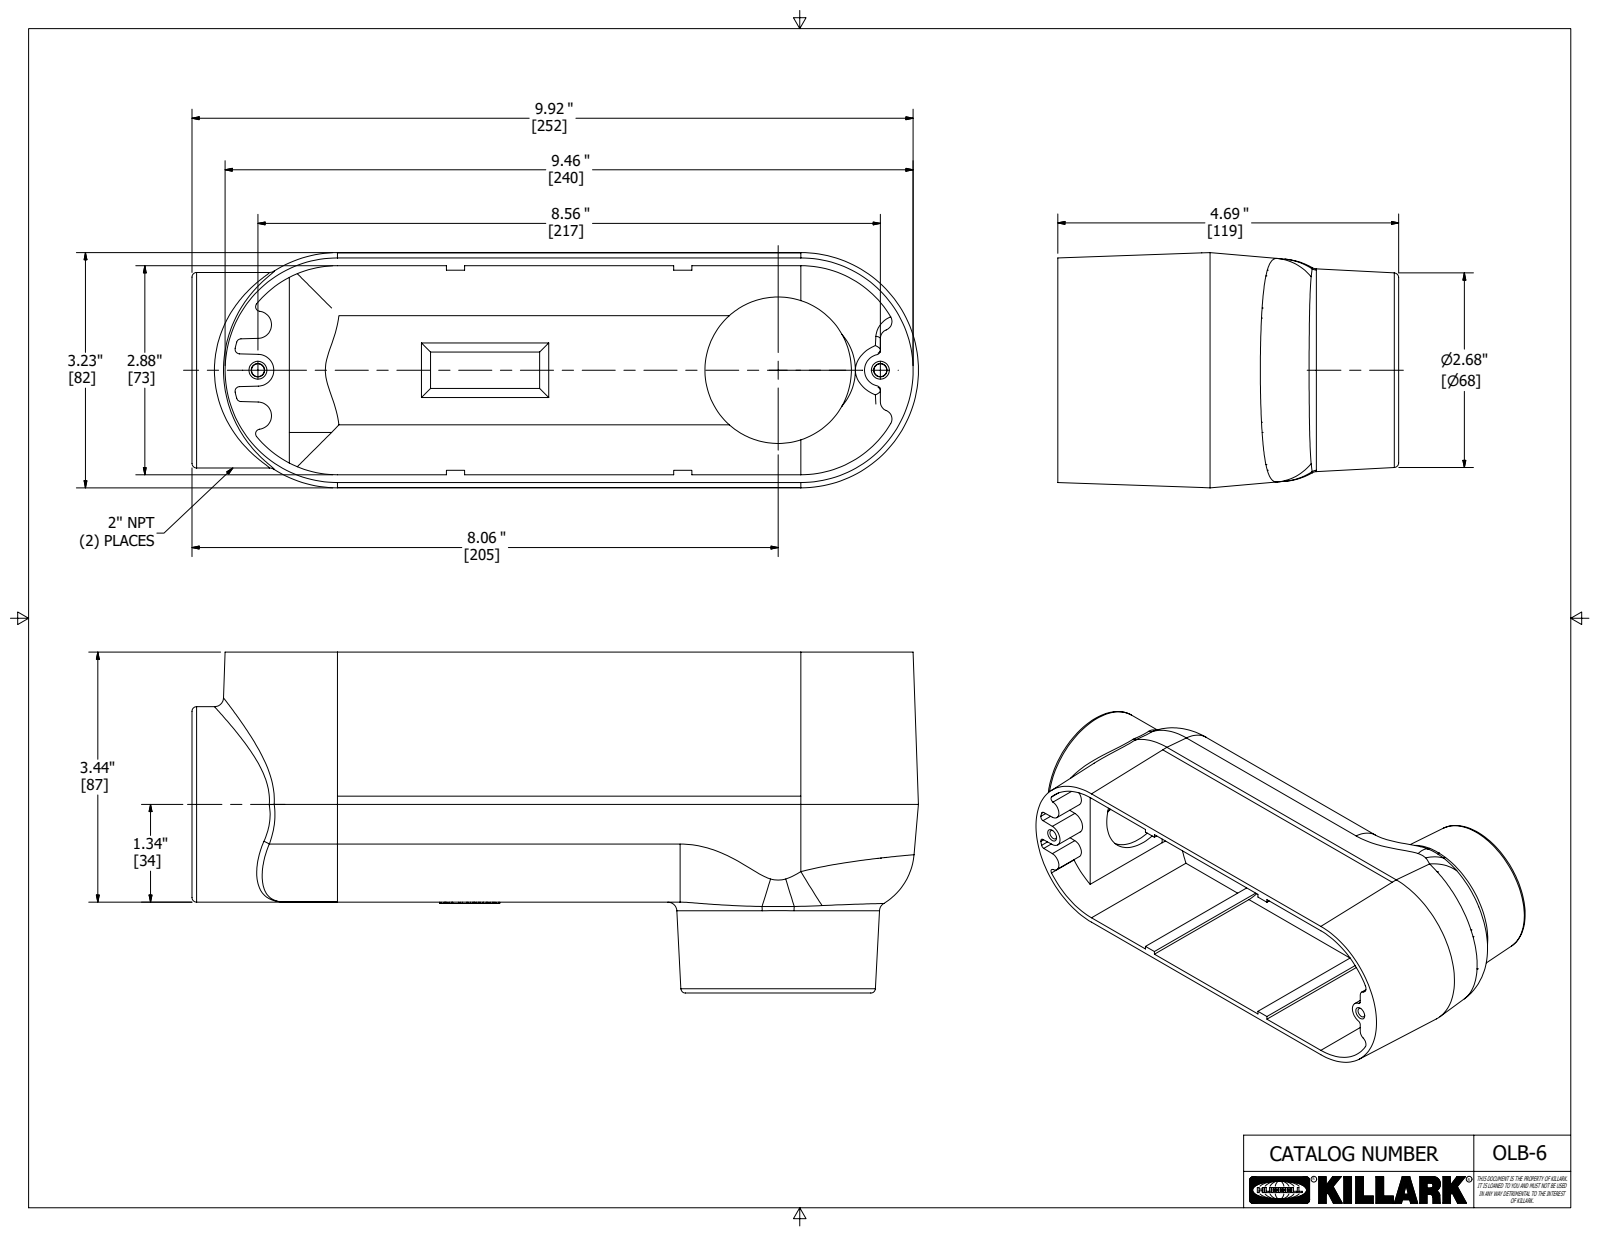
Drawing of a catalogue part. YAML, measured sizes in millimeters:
part_name: "13061-1"
step_written_by: "Autodesk Inventor 2018 (AUTOMOTIVE_DESIGN)"
units: millimeters
bodies: {solids: 1, faces: 369, planar: 180, cylindrical: 33, other: 156}
overall_size: [253.8, 119.1, 82.2]
volume: 320400
surface_area: 138800
round_holes:
  - {diameter: 51.2, count: 2}
round_bosses_or_shafts:
  - {diameter: 68.3, count: 1}
partial_cylinders:
  - {radius: 1.6, count: 8}
  - {radius: 3.2, count: 6}
  - {radius: 17.4, count: 3}
  - {radius: 4.7, count: 2}
  - {radius: 5.6, count: 2}
  - {radius: 22.2, count: 2}
  - {radius: 36.5, count: 2}
face_to_face_distances: [73, 3.2, 87.3, 84.2, 1.6, 71.4, 69.9, 206.5, 30.5, 0.8]
